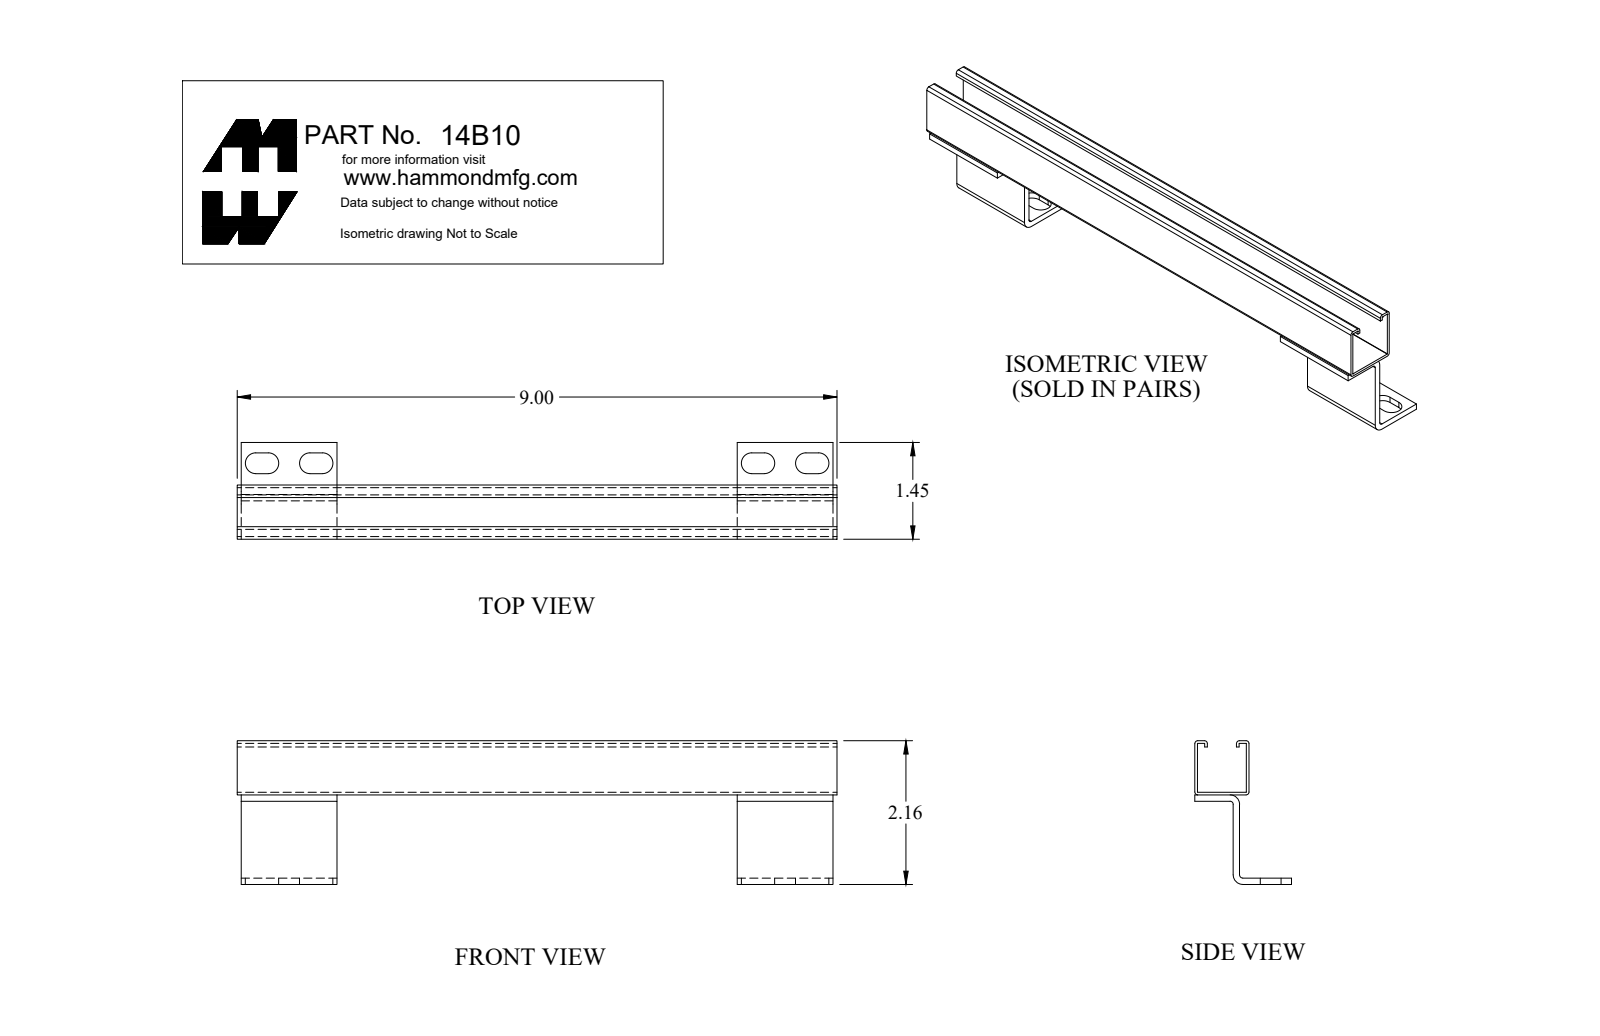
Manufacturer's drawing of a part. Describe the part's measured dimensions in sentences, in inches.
The part is named "14B10". Its 3-D file was written by "SolidWorks 2018 (AUTOMOTIVE_DESIGN)". It is 3 solids with 74 faces: 46 planar, 28 cylindrical and 0 other. Overall it measures 9 by 2.156 by 1.451 inches. Its volume is 1.637 cubic inches and its surface area 65.62 square inches. Partial cylindrical surfaces (rounded edges, fillets, slot ends): 8 of radius 0.156, 6 of radius 0.043, 2 of radius 0.048, 2 of radius 0.143. The main face-to-face distances are 0.04, 0.773, 0.813, 0.733, 0.095, 0.773, 1.248, 0.142, 0.237, 0.102.
